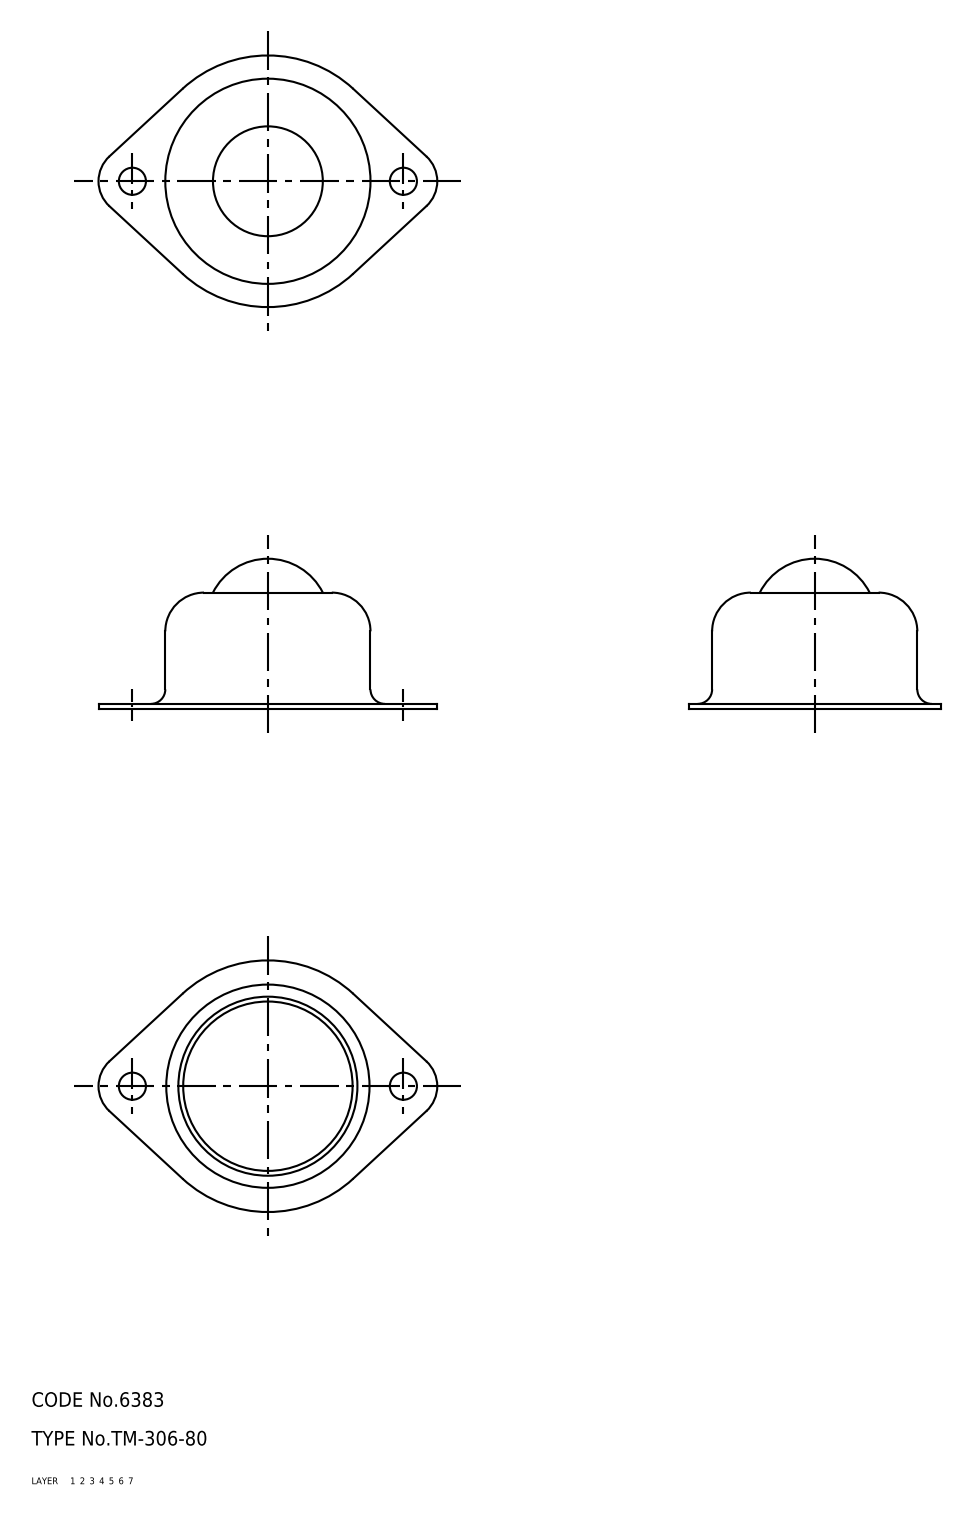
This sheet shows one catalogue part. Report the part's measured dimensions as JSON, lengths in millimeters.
{"part_name": "67113366; 67113379; 67113392", "step_written_by": "CADfix (AUTOMOTIVE_DESIGN)", "units": "millimeters", "bodies": {"solids": 3, "faces": 53, "planar": 0, "cylindrical": 0, "other": 53}, "overall_size": [70, 52, 31], "volume_mm3": 21067, "surface_area_mm2": 18463}
